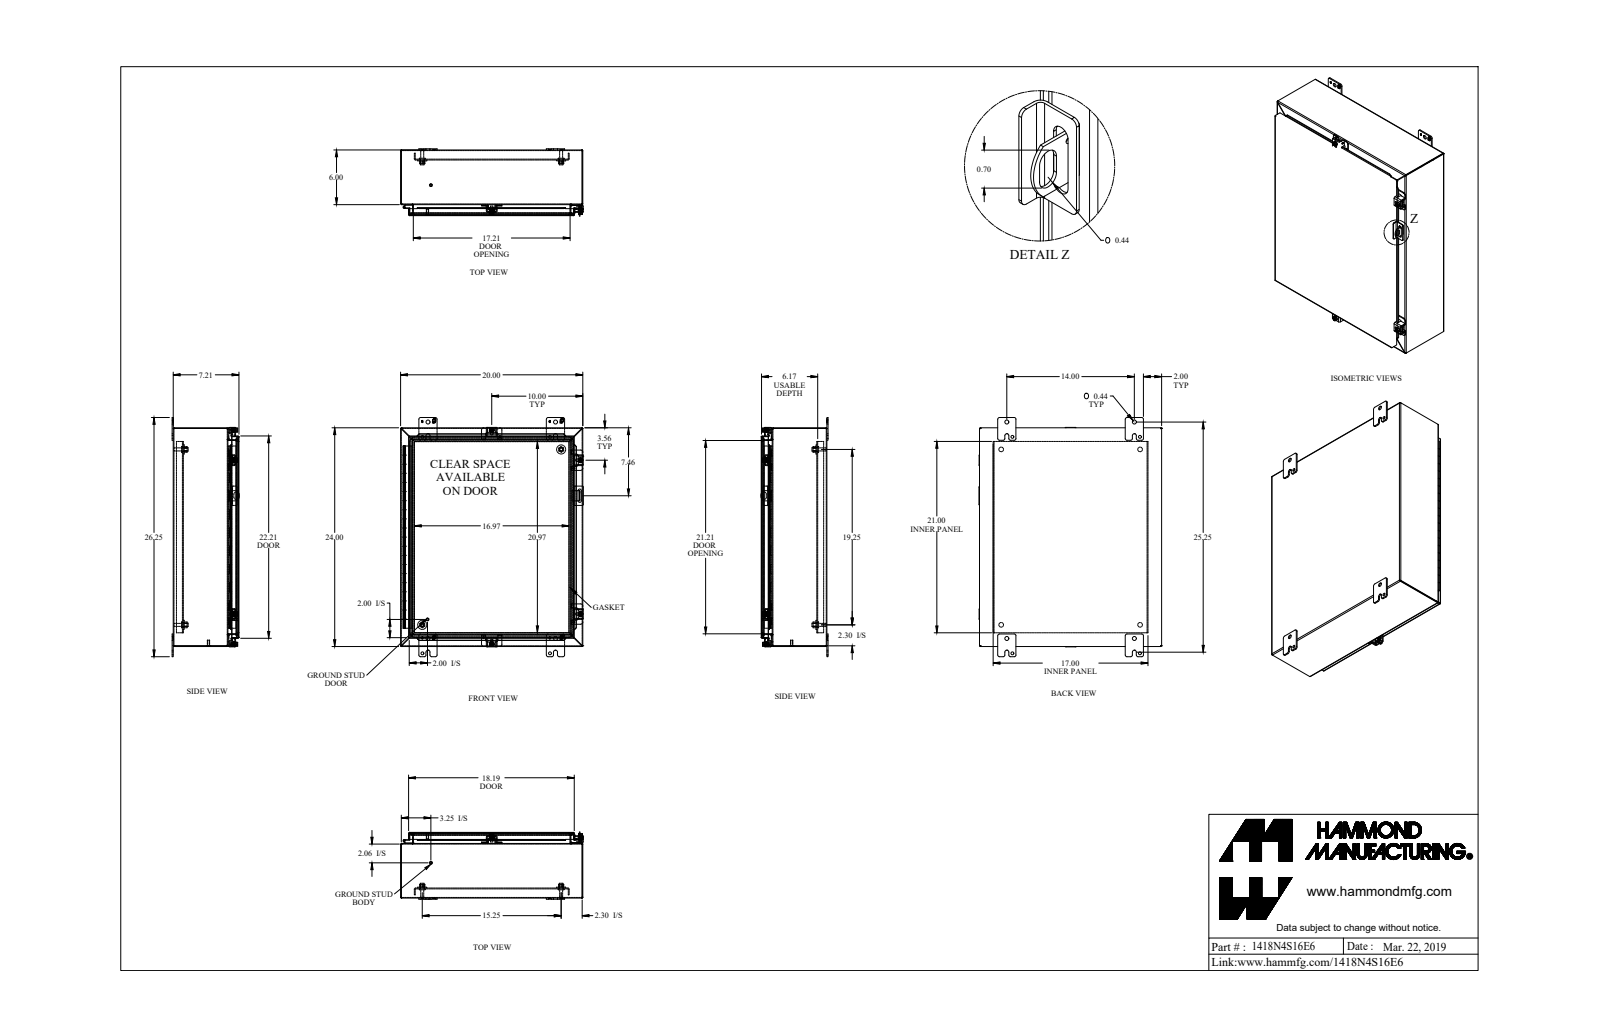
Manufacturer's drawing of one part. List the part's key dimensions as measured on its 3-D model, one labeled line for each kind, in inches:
Part name (STEP PRODUCT): 1418N4S16E6_Default
STEP written by: SolidWorks 2019 (CONFIG_CONTROL_DESIGN)
Units: inches
Bodies: 39 solids, 1374 faces (746 planar, 494 cylindrical, 134 other)
Overall size (bounding box): 26.25 × 20.063 × 7.375
Volume: 171.7 in³ · Surface area: 4 508 in²
Round holes (diameter × count): ⌀0.213 ×4, ⌀0.313 ×4, ⌀0.375 ×4, ⌀0.437 ×4, ⌀0.5 ×4, ⌀0.265 ×2, ⌀0.265 ×2, ⌀0.307 ×2, ⌀0.445 ×2, ⌀0.11 ×1, ⌀0.125 ×1
Round bosses / shafts (diameter × count): ⌀0.65 ×4, ⌀0.5 ×4, ⌀0.39 ×4, ⌀0.375 ×4, ⌀0.332 ×4, ⌀0.244 ×4, ⌀1 ×2, ⌀0.313 ×2
Partial cylindrical surfaces — rounded edges, fillets, slot ends (radius × count): R0.188 ×26, R0.036 ×24, R0.108 ×24, R0.048 ×21, R0.143 ×21, R0.25 ×20, R0.125 ×12, R0.045 ×8
Main face-to-face distances: 0.072, 7.066, 7.138, 0.072, 7.138, 7.21, 0.937, 0.095, 1.009, 6.106
Hole centre spacings: 7.916, 22.694, 14, 24.559, 1.735, 2.434, 14.702, 15.25
